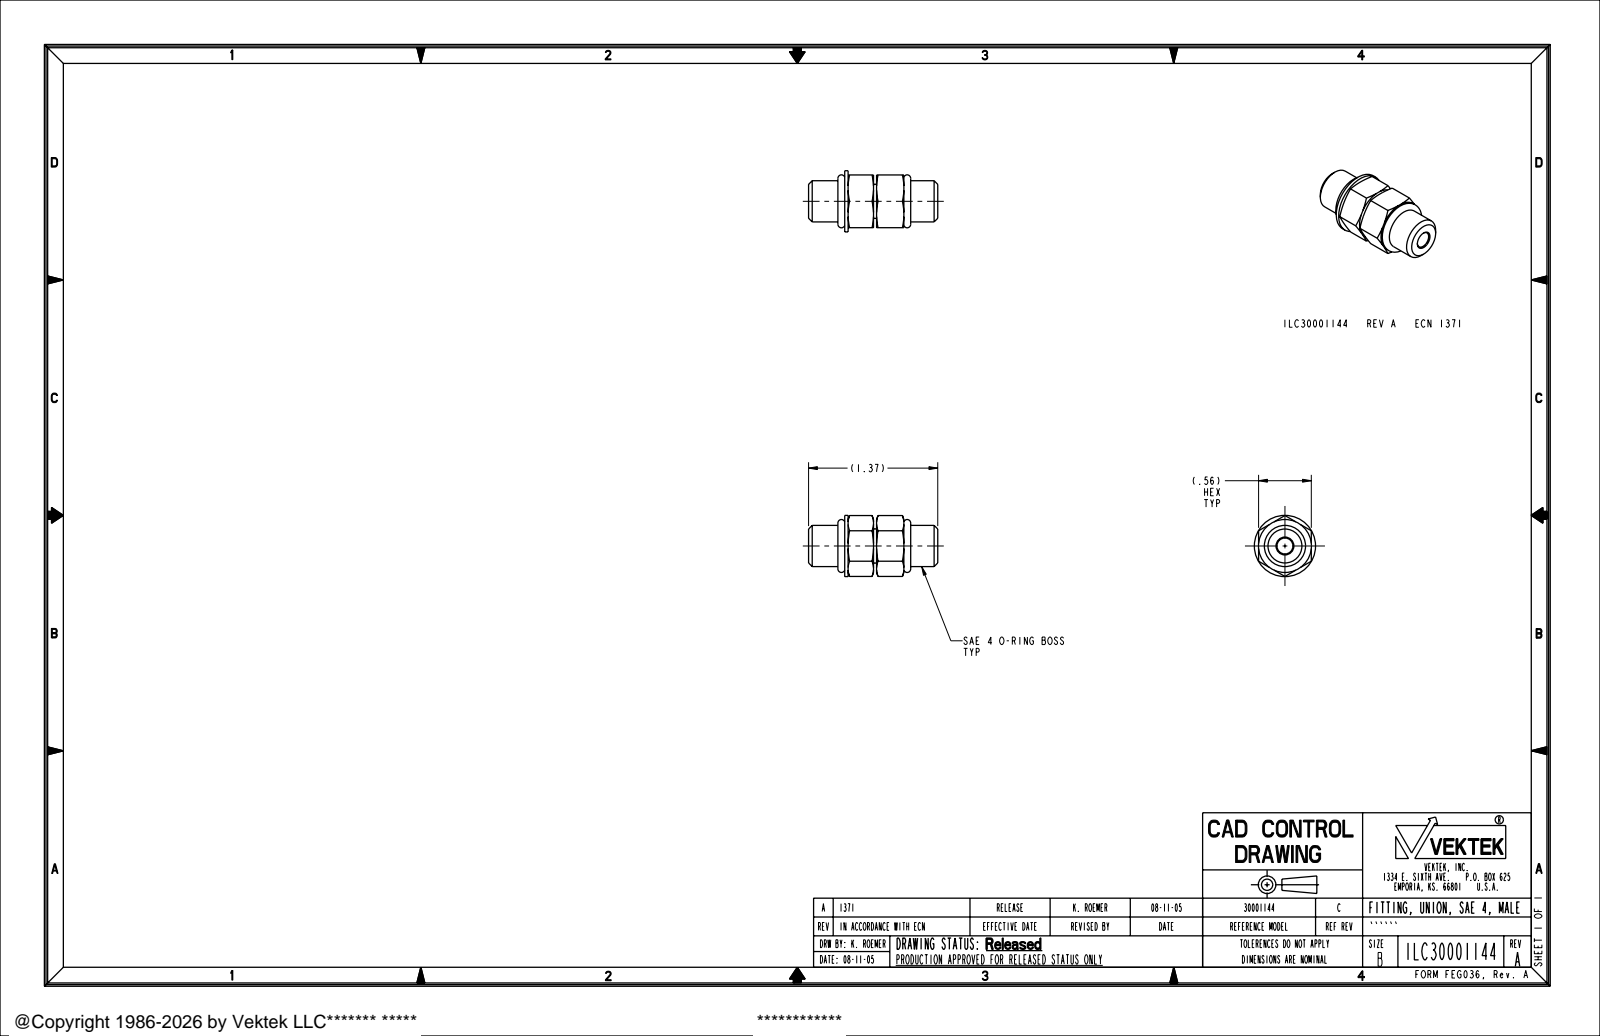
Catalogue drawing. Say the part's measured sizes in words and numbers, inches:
The part is named "ILC30001144". Its 3-D file was written by "PRO/ENGINEER BY PARAMETRIC TECHNOLOGY CORPORATION, 2004290 (AUTOMOTIVE_DESIGN_CC2)". It is 1 solid with 75 faces: 21 planar, 14 cylindrical and 40 other. Overall it measures 1.372 by 0.65 by 0.65 inches. Its volume is 0.258 cubic inches and its surface area 4.078 square inches. Round holes: 1 of diameter 0.17. Round bosses or shafts: 1 of diameter 0.65, 1 of diameter 0.437, 1 of diameter 0.363. The main face-to-face distances are 0.56, 0.032, 0.306, 0.339, 0.036, 0.27, 0.302, 0.989, 0.952, 0.682.
